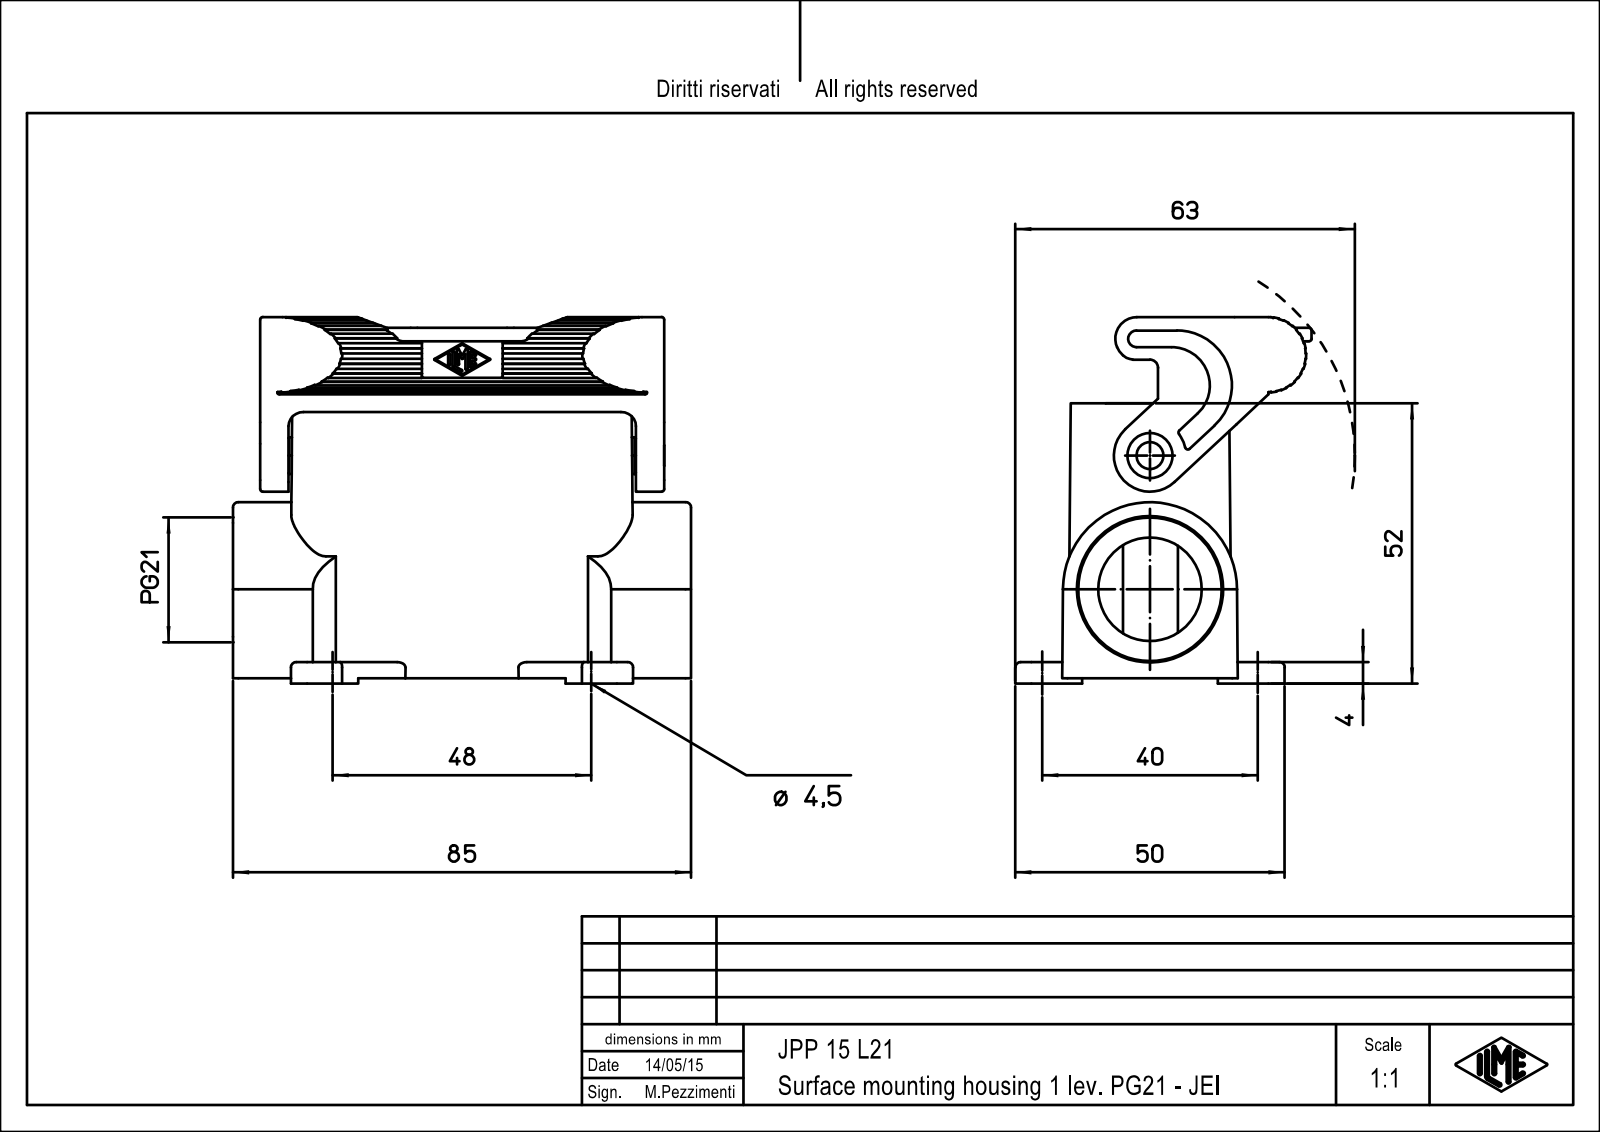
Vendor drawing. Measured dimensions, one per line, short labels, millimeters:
name: CZP_15; LEVA_JP15; JPP_15_L21
written by: Creo Elements/Direct Modeling 18.1F 24-Jul-2014 (C) Parametric Technology GmbH (AUTOMOTIVE_DESIGN)
unit: mm
bodies: 2 solids, 451 faces (188 planar, 195 cylindrical, 68 other)
size: 85 × 68 × 55
volume: 55 230 mm³; area: 34 039 mm²
holes: 4× ⌀3, 4× ⌀4.5, 1× ⌀5, 1× ⌀8.4, 1× ⌀22
bosses: 1× ⌀6.8, 1× ⌀4.8
rounds: 36× R0.5, 15× R0.2, 12× R1, 11× R3, 4× R6.5, 3× R0.1, 2× R0.3, 2× R2.8
face distances: 24.2, 3, 30.6, 6.4, 1.15, 10.25, 74.75, 10.5, 54, 13.6
hole spacings: 12.02, 28.01, 50.21, 56.22, 16, 40, 48, 49.5
